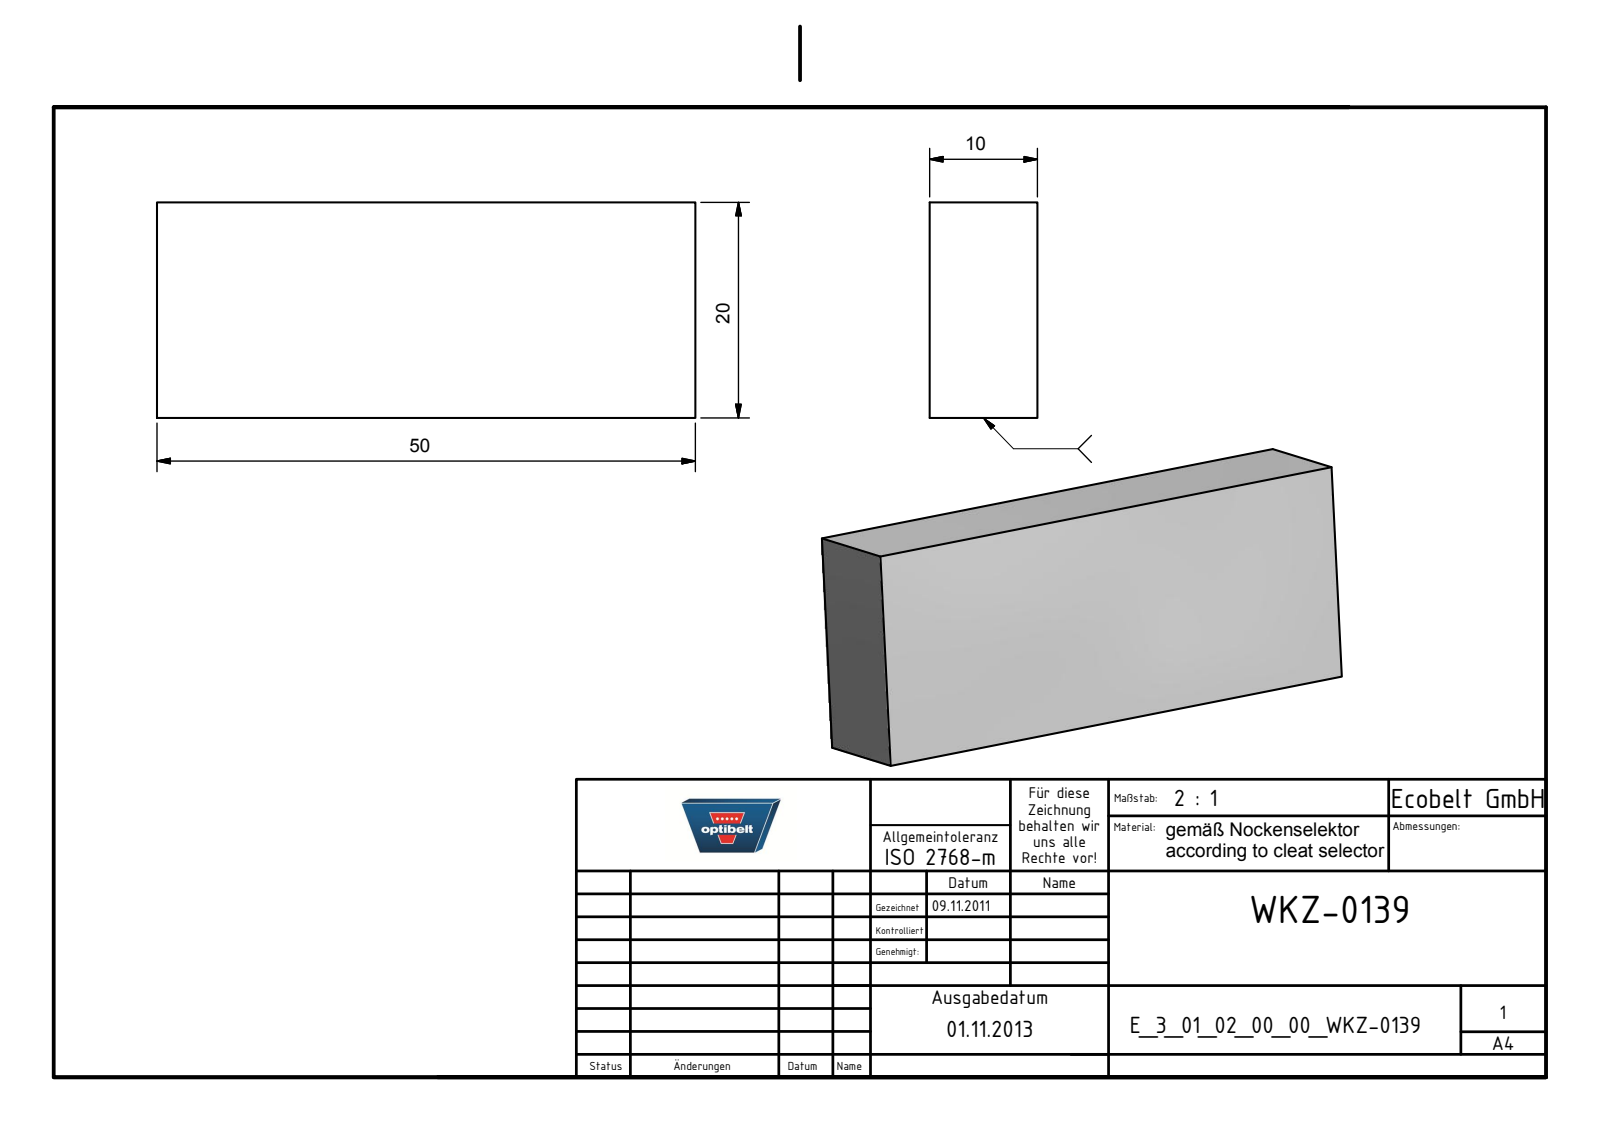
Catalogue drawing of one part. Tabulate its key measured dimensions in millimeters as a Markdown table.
| quantity | value |
| --- | --- |
| part name | E_3_01_02_00_00_WKZ-0139 |
| STEP written by | Autodesk Inventor 2021 (AUTOMOTIVE_DESIGN) |
| units | millimeters |
| bodies | 1 solid, 6 faces (6 planar, 0 cylindrical, 0 other) |
| overall size | 50 × 20 × 10 |
| volume | 10 000 mm³ |
| surface area | 3 400 mm² |
| main face-to-face distances | 10, 20, 50 |
